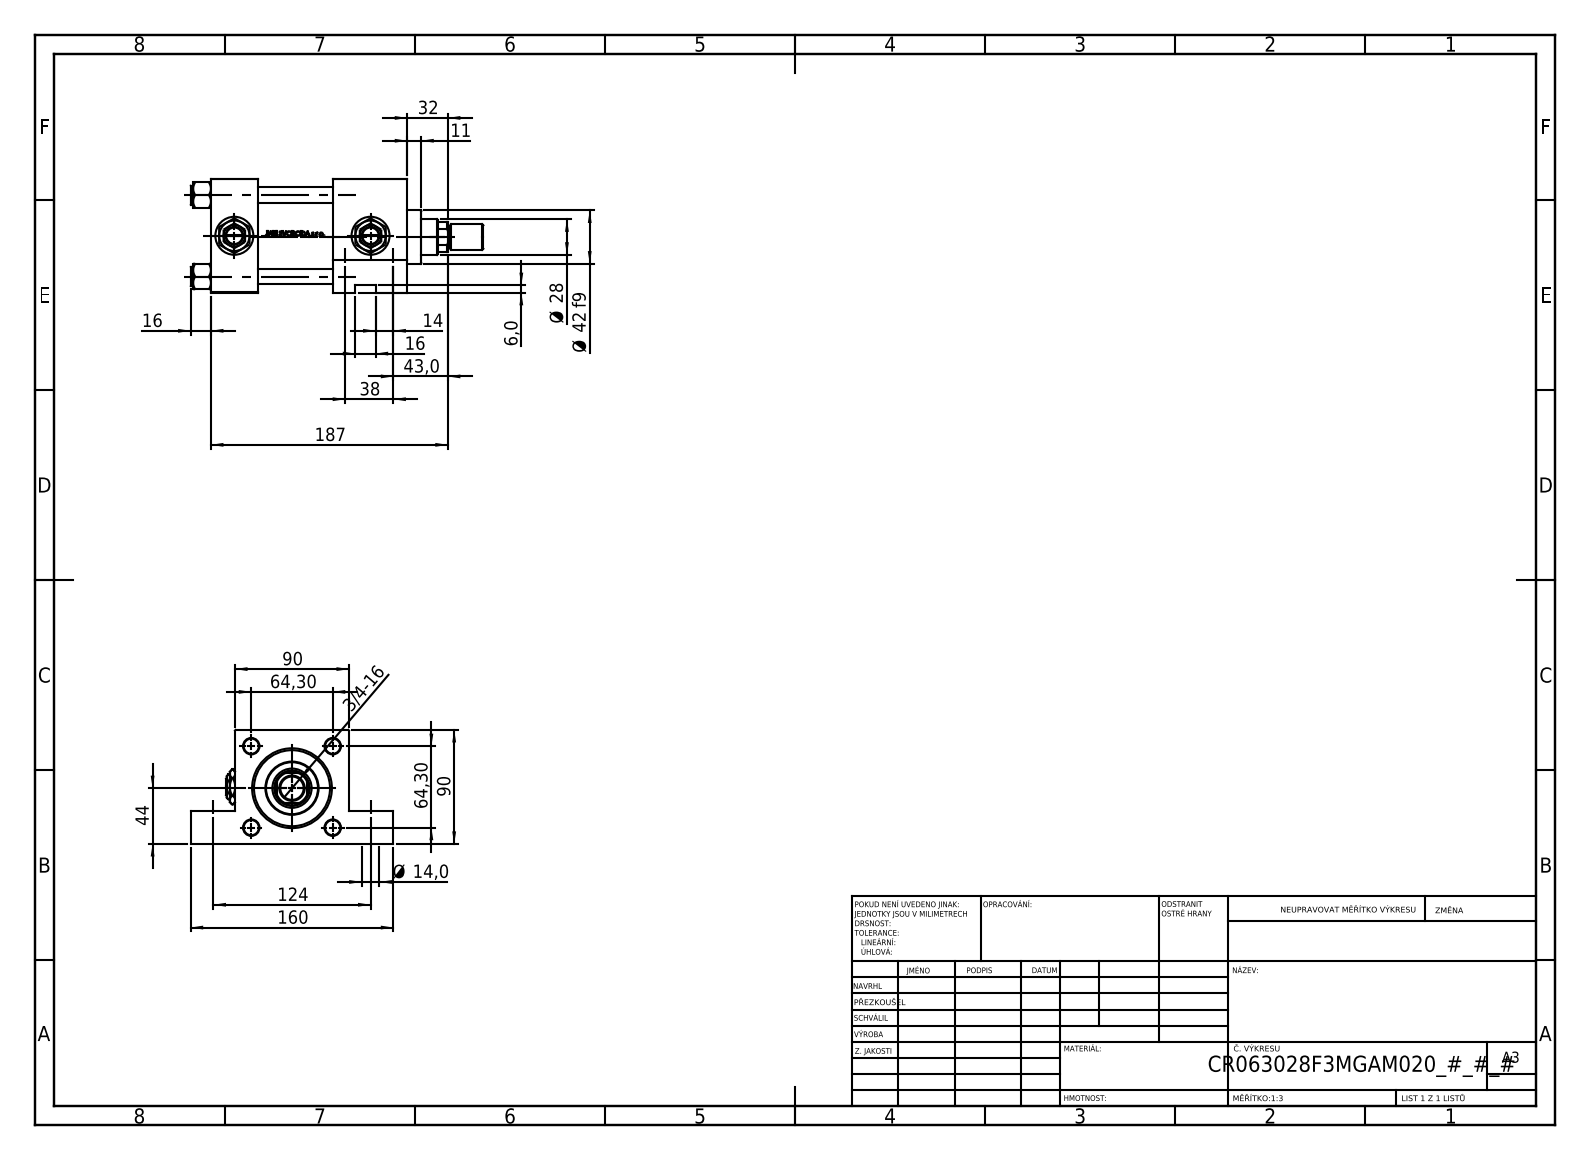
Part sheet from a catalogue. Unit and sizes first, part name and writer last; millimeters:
Units: millimetres
Overall size (bounding box): 231 × 160 × 90
Round holes (diameter × count): ⌀12 ×4, ⌀20.96 ×4, ⌀30 ×4, ⌀7 ×3, ⌀14 ×2, ⌀14 ×2, ⌀18.5 ×1, ⌀28 ×1, ⌀31 ×1, ⌀50 ×1, ⌀60 ×1, ⌀63 ×1
Round bosses / shafts (diameter × count): ⌀15 ×4, ⌀69 ×1, ⌀42 ×1, ⌀20 ×1, ⌀18 ×1
Partial cylindrical surfaces — rounded edges, fillets, slot ends (radius × count): R13.5 ×1
Main face-to-face distances: 90, 59, 37, 155, 118, 96, 20, 64, 26, 125
Hole centre spacings: 64.3, 38, 44.77, 46.18, 62.8, 68.03, 90.93, 107.24
Volume: 1 031 000 mm³ · Surface area: 201 188 mm²
Bodies: 14 solids, 1217 faces (489 planar, 140 cylindrical, 588 other)
Part name (STEP PRODUCT): V215CR_F_TYCINKA; V215_VC_A; NUT_M5_F; ROD_END_AH (+3 more)
STEP written by: SolidWorks 2019 (CONFIG_CONTROL_DESIGN)
